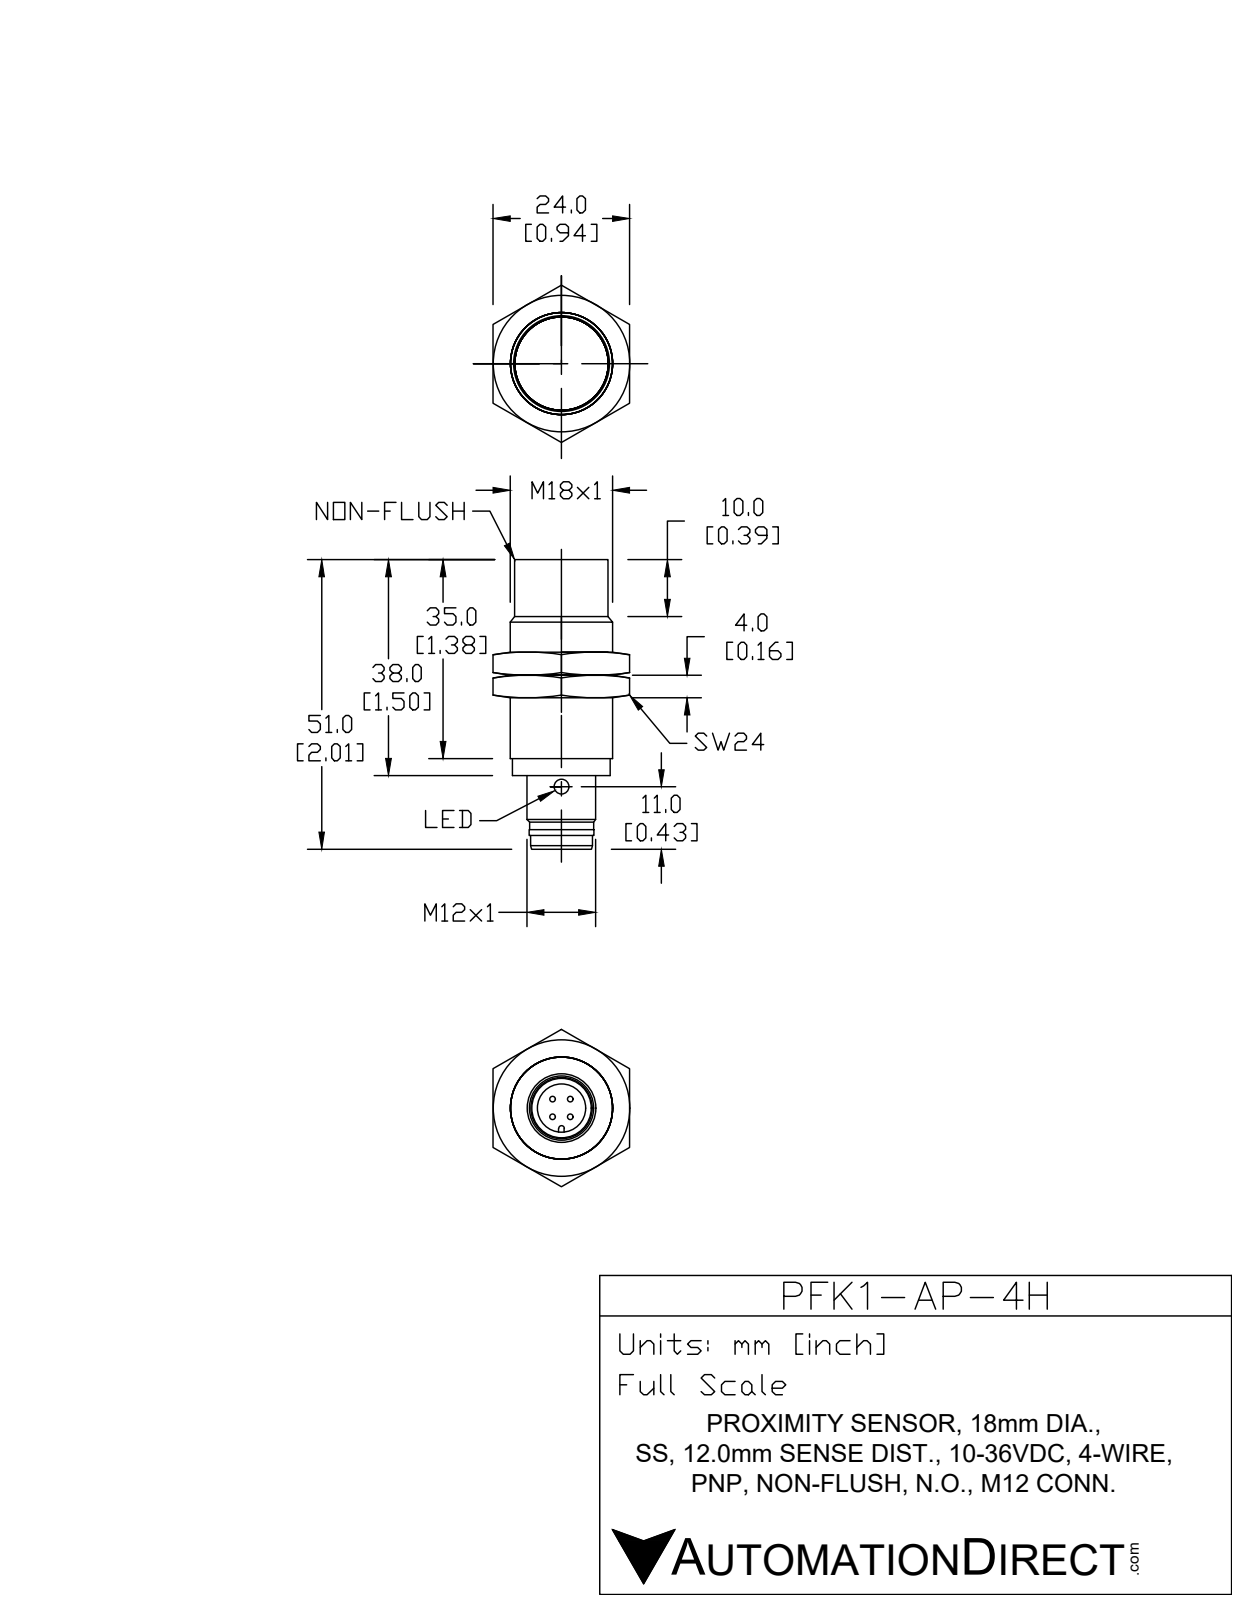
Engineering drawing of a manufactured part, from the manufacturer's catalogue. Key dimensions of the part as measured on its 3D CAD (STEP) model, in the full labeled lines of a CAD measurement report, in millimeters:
Part name (STEP PRODUCT): PFK1-AP-4H
STEP written by: SolidWorks 2017 (AUTOMOTIVE_DESIGN)
Units: millimetres
Bodies: 3 solids, 114 faces (25 planar, 34 cylindrical, 55 other)
Overall size (bounding box): 51 × 27.7 × 24
Volume: 11 900 mm³ · Surface area: 5 292 mm²
Round holes (diameter × count): ⌀2.5 ×2, ⌀8.4 ×1, ⌀16.9 ×1
Round bosses / shafts (diameter × count): ⌀18 ×1, ⌀16.9 ×1, ⌀16.6 ×1, ⌀16 ×1, ⌀12 ×1, ⌀11.3 ×1, ⌀10.6 ×1
Partial cylindrical surfaces — rounded edges, fillets, slot ends (radius × count): R0.6 ×1, R5 ×1
Main face-to-face distances: 4, 17, 21, 24, 8, 25, 13, 38, 4.1, 17.1
